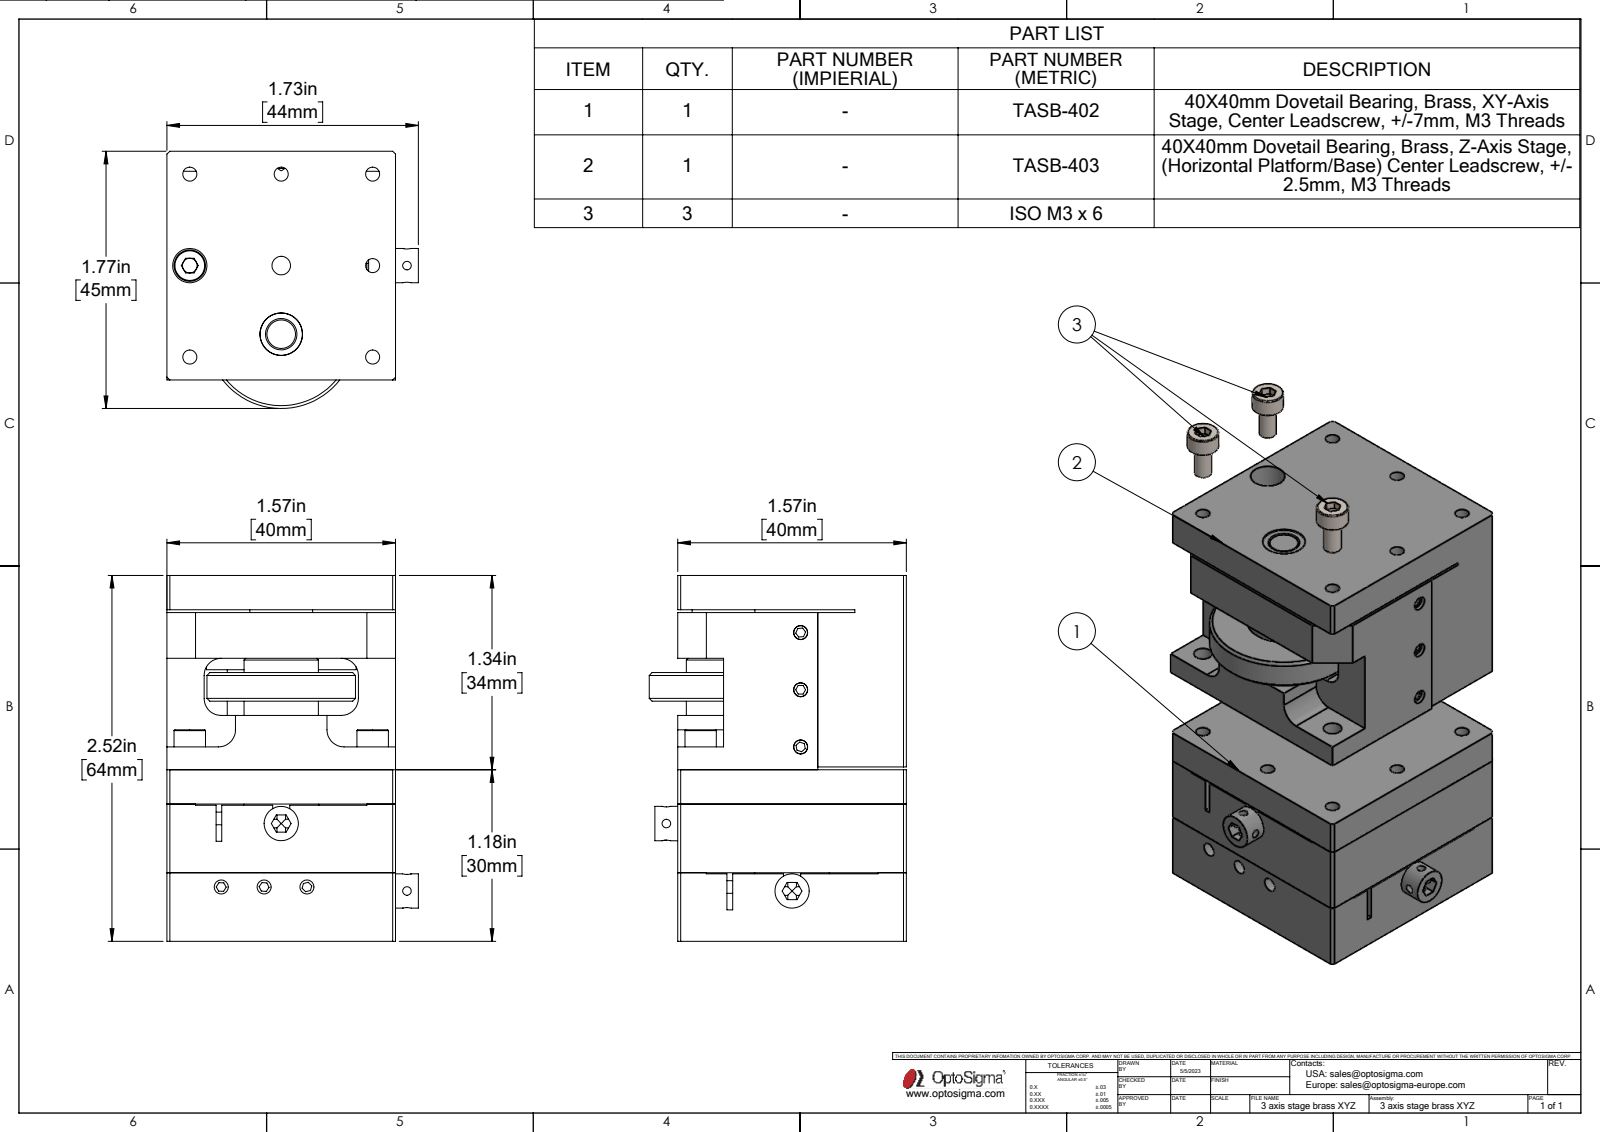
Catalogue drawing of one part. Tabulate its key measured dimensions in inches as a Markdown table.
| quantity | value |
| --- | --- |
| part name | socket head cap screw_iso_ISO 4762 M3 x 6 - 6N; TASB-402; TASB-402(2); TAS-402-C1B-S02 (+4 more) |
| STEP written by | SolidWorks 2023 (AUTOMOTIVE_DESIGN) |
| units | inches |
| bodies | 9 solids, 760 faces (384 planar, 220 cylindrical, 156 other) |
| overall size | 2.52 × 1.772 × 1.732 |
| volume | 5.405 in³ |
| surface area | 65.43 in² |
| round holes (diameter × count) | 0.097 × 7, 0.097 × 6, 0.059 × 5, 0.236 × 5, 0.126 × 4, 0.128 × 4, 0.063 × 1, 0.098 × 1, 0.165 × 1, 0.197 × 1, 0.217 × 1, 0.294 × 1 |
| round bosses / shafts (diameter × count) | 0.087 × 9, 0.118 × 8, 0.217 × 7, 0.236 × 2, 0.157 × 2, 1.024 × 1, 0.512 × 1, 0.433 × 1 |
| partial cylindrical surfaces (radius × count) | 0.079 × 12, 0.118 × 6, 0.098 × 4, 0.059 × 3, 0.039 × 2 |
| main face-to-face distances | 0.472, 1.575, 0.256, 0.02, 0.236, 1.339, 0.945, 1.083, 1.181, 0.709 |
| hole center spacings | 0.63, 1.26, 0.891, 1.409, 1.071, 0.649, 0.673, 1.623 |
